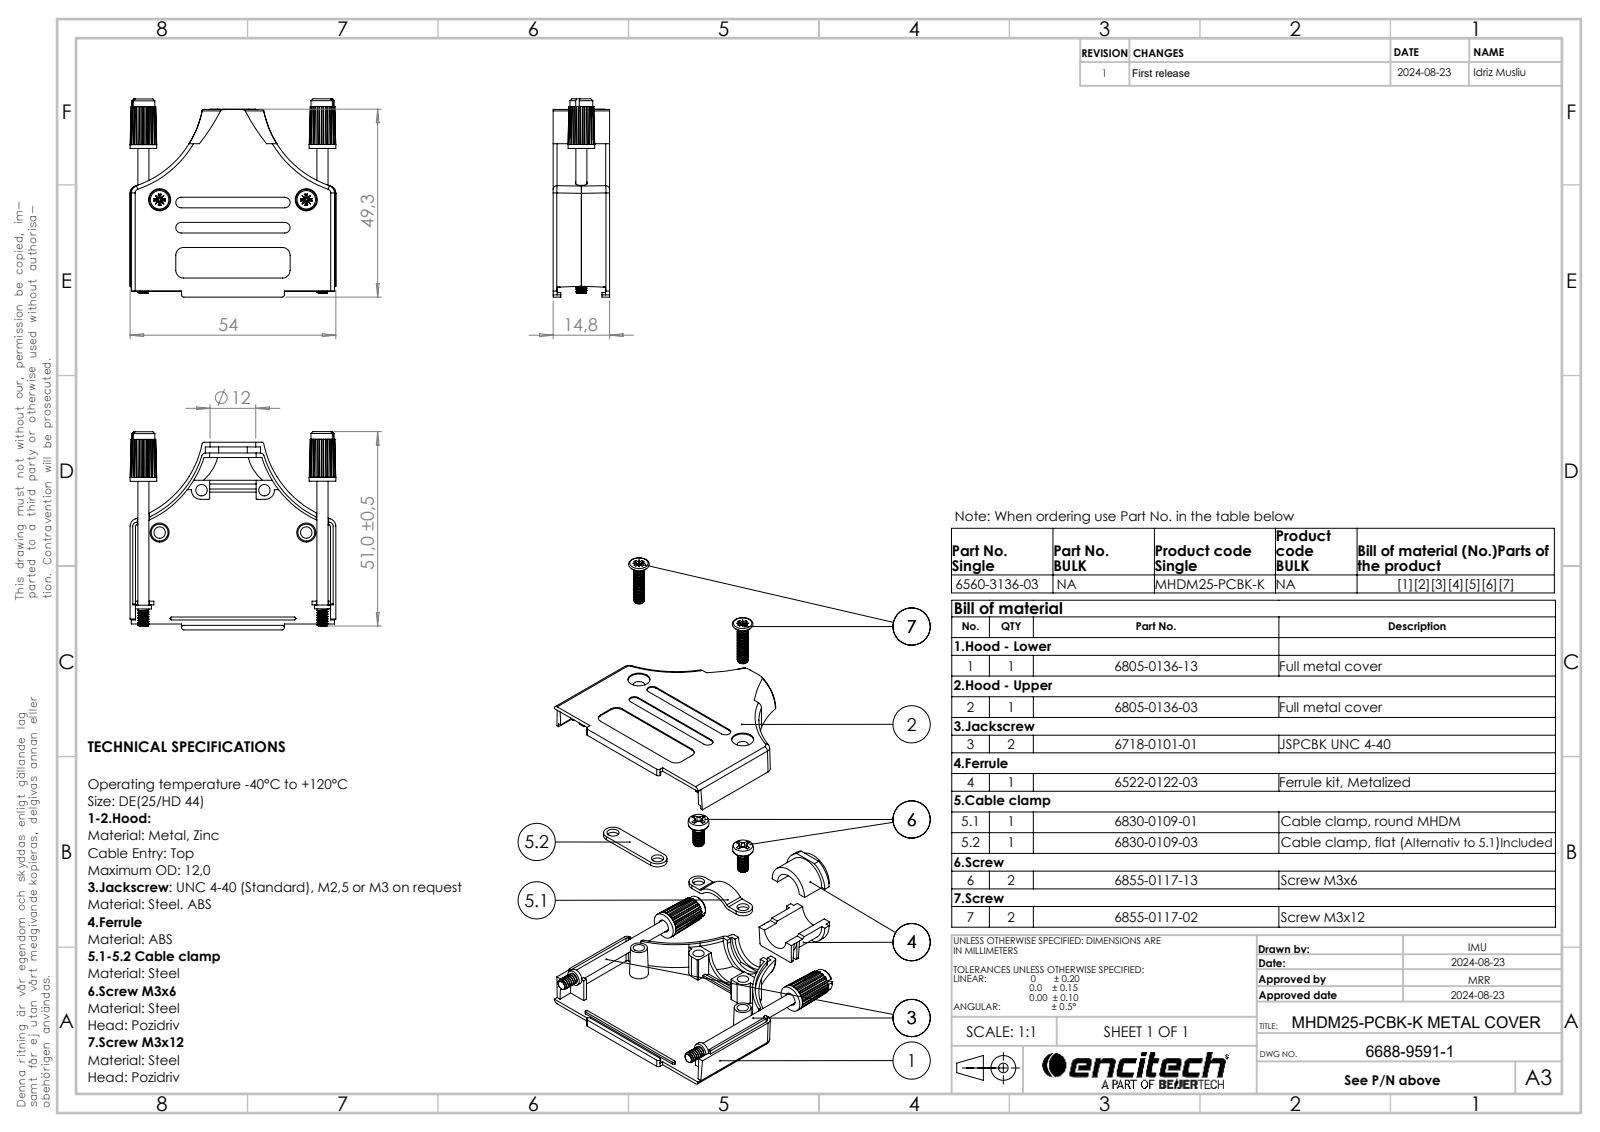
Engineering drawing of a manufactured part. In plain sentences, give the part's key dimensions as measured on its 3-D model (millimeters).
The part is named "6805-0136-13; 6560-0136-03; 6855-0117-02; 6522-0122-03 (8mm LV) (+5 more)". Its 3-D file was written by "SolidWorks 2021 (AUTOMOTIVE_DESIGN)". It is 11 solids with 844 faces: 411 planar, 333 cylindrical and 100 other. Overall it measures 54 by 49.3 by 14.8 millimeters. Its volume is 8 763 cubic millimeters and its surface area 16 387 square millimeters. Round holes: 4 of diameter 3, 4 of diameter 3.2, 2 of diameter 4.5, 2 of diameter 5.8, 1 of diameter 8, 1 of diameter 12.2. Round bosses or shafts: 4 of diameter 2.9, 2 of diameter 5, 2 of diameter 4, 2 of diameter 3, 2 of diameter 2.8, 1 of diameter 12. Partial cylindrical surfaces (rounded edges, fillets, slot ends): 14 of radius 1, 10 of radius 26.4, 8 of radius 0.1, 4 of radius 0.2, 4 of radius 0.5, 4 of radius 1.4, 4 of radius 2, 3 of radius 0.25. The main face-to-face distances are 13.75, 1.05, 12.7, 14.8, 0.75, 14.5, 13.45, 6.35, 7.4, 7.1. The hole center spacings are 15.64, 23.5, 29.66, 16.5, 38.5, 47.
